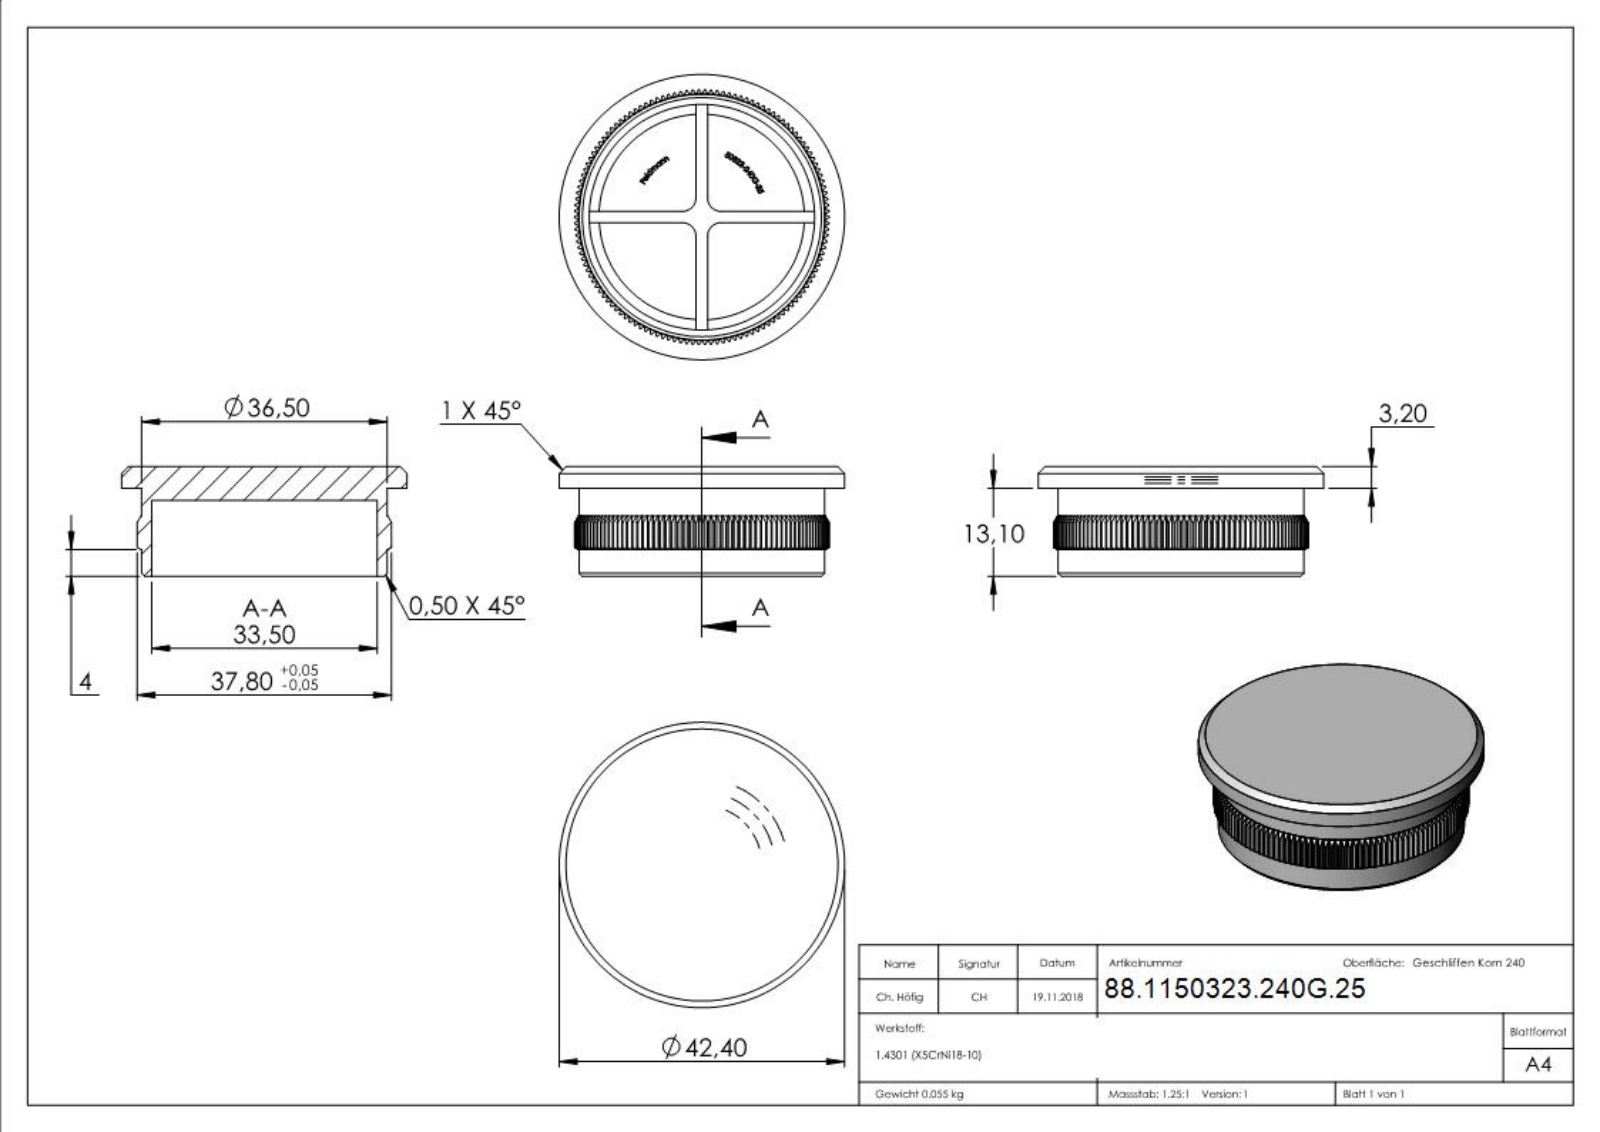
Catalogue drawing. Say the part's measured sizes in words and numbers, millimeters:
The part is named "50323-240G-25". Its 3-D file was written by "SolidWorks 2015 (CONFIG_CONTROL_DESIGN)". It is 1 solid with 1225 faces: 678 planar, 142 cylindrical and 405 other. Overall it measures 42.4 by 42.4 by 16.3 millimeters. Its volume is 6 901 cubic millimeters and its surface area 6 704 square millimeters. Round holes: 1 of diameter 33.5. Round bosses or shafts: 1 of diameter 42.4, 1 of diameter 36.5. Partial cylindrical surfaces (rounded edges, fillets, slot ends): 4 of radius 2, 1 of radius 18.9. The main face-to-face distances are 3, 3.2, 18.24, 18.26, 5, 1.8, 2, 1.7, 11.3, 13.1.
